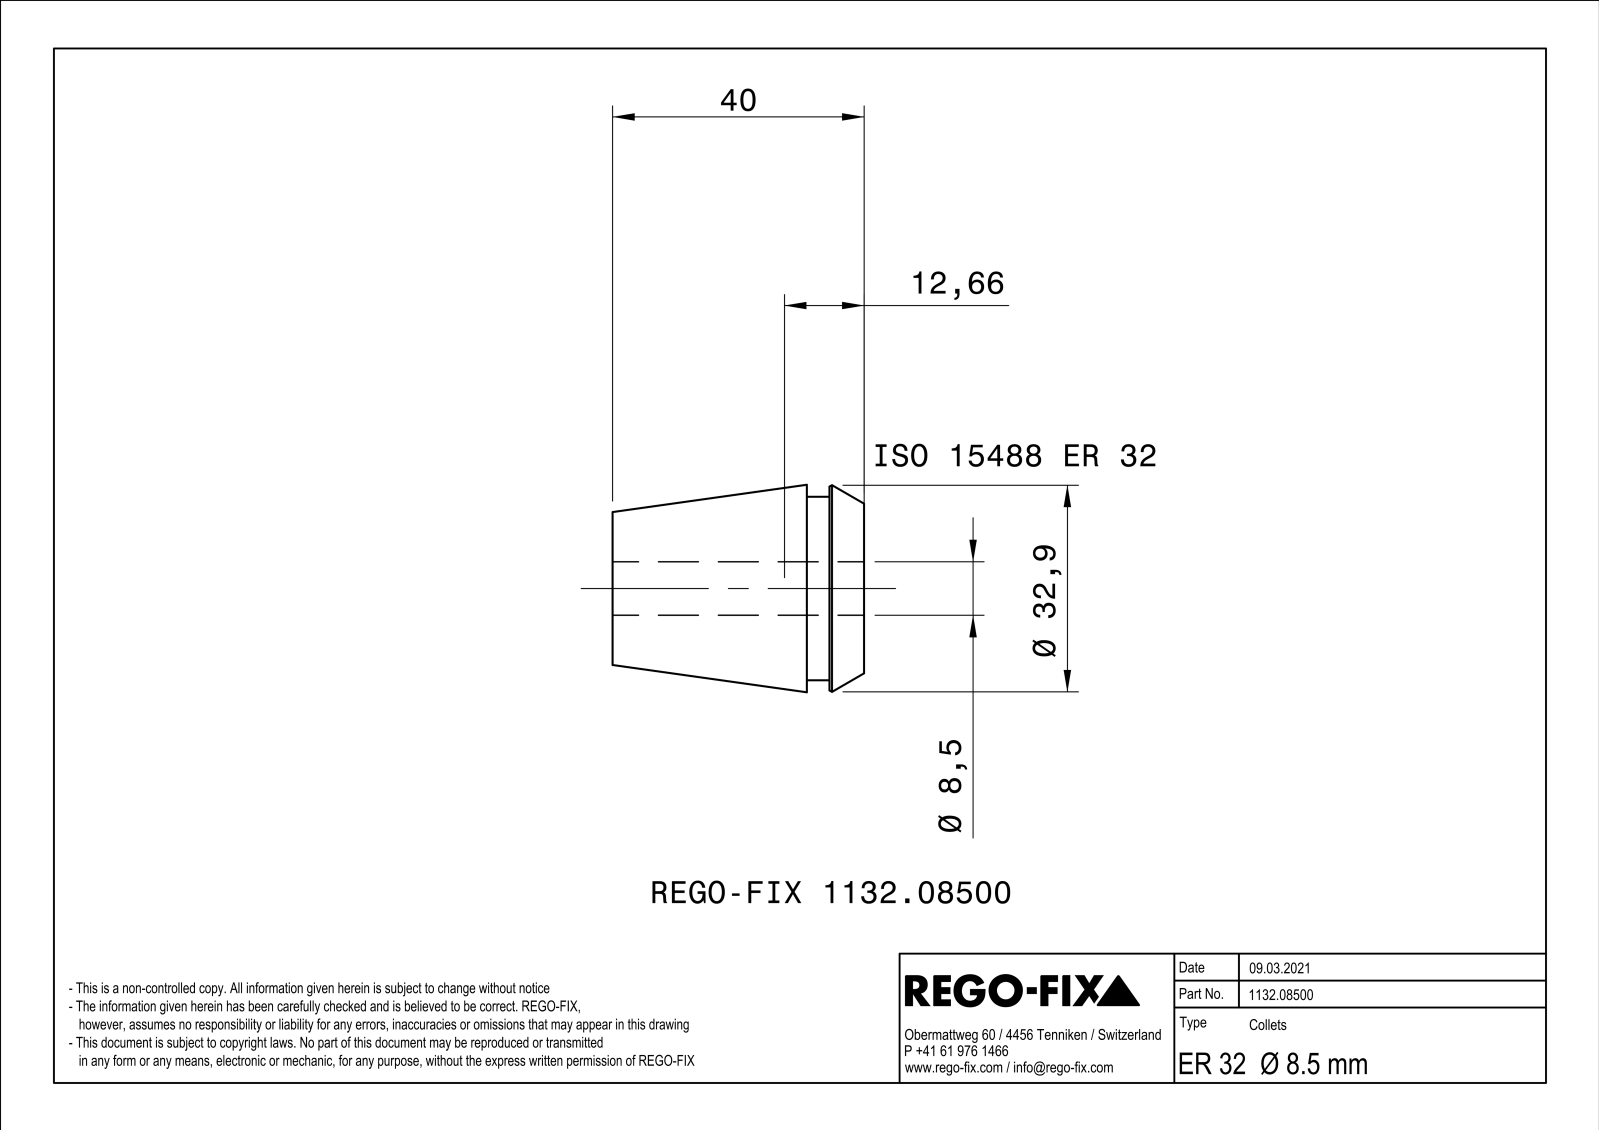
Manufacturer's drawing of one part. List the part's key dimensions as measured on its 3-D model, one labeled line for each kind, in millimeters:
Part name (STEP PRODUCT): NOCUT
STEP written by: SIEMENS PLM Software Solid Edge ST10 (AUTOMOTIVE_DESIGN)
Units: millimetres
Bodies: 1 solid, 177 faces (72 planar, 25 cylindrical, 80 other)
Overall size (bounding box): 40 × 32.99 × 32.99
Volume: 19 514 mm³ · Surface area: 16 709 mm²
Round holes (diameter × count): ⌀8.5 ×1
Round bosses / shafts (diameter × count): ⌀29.2 ×1
Partial cylindrical surfaces — rounded edges, fillets, slot ends (radius × count): R0.4 ×8
Main face-to-face distances: 0.8, 40, 9.1, 30.9, 5.5, 3.6, 34.5
